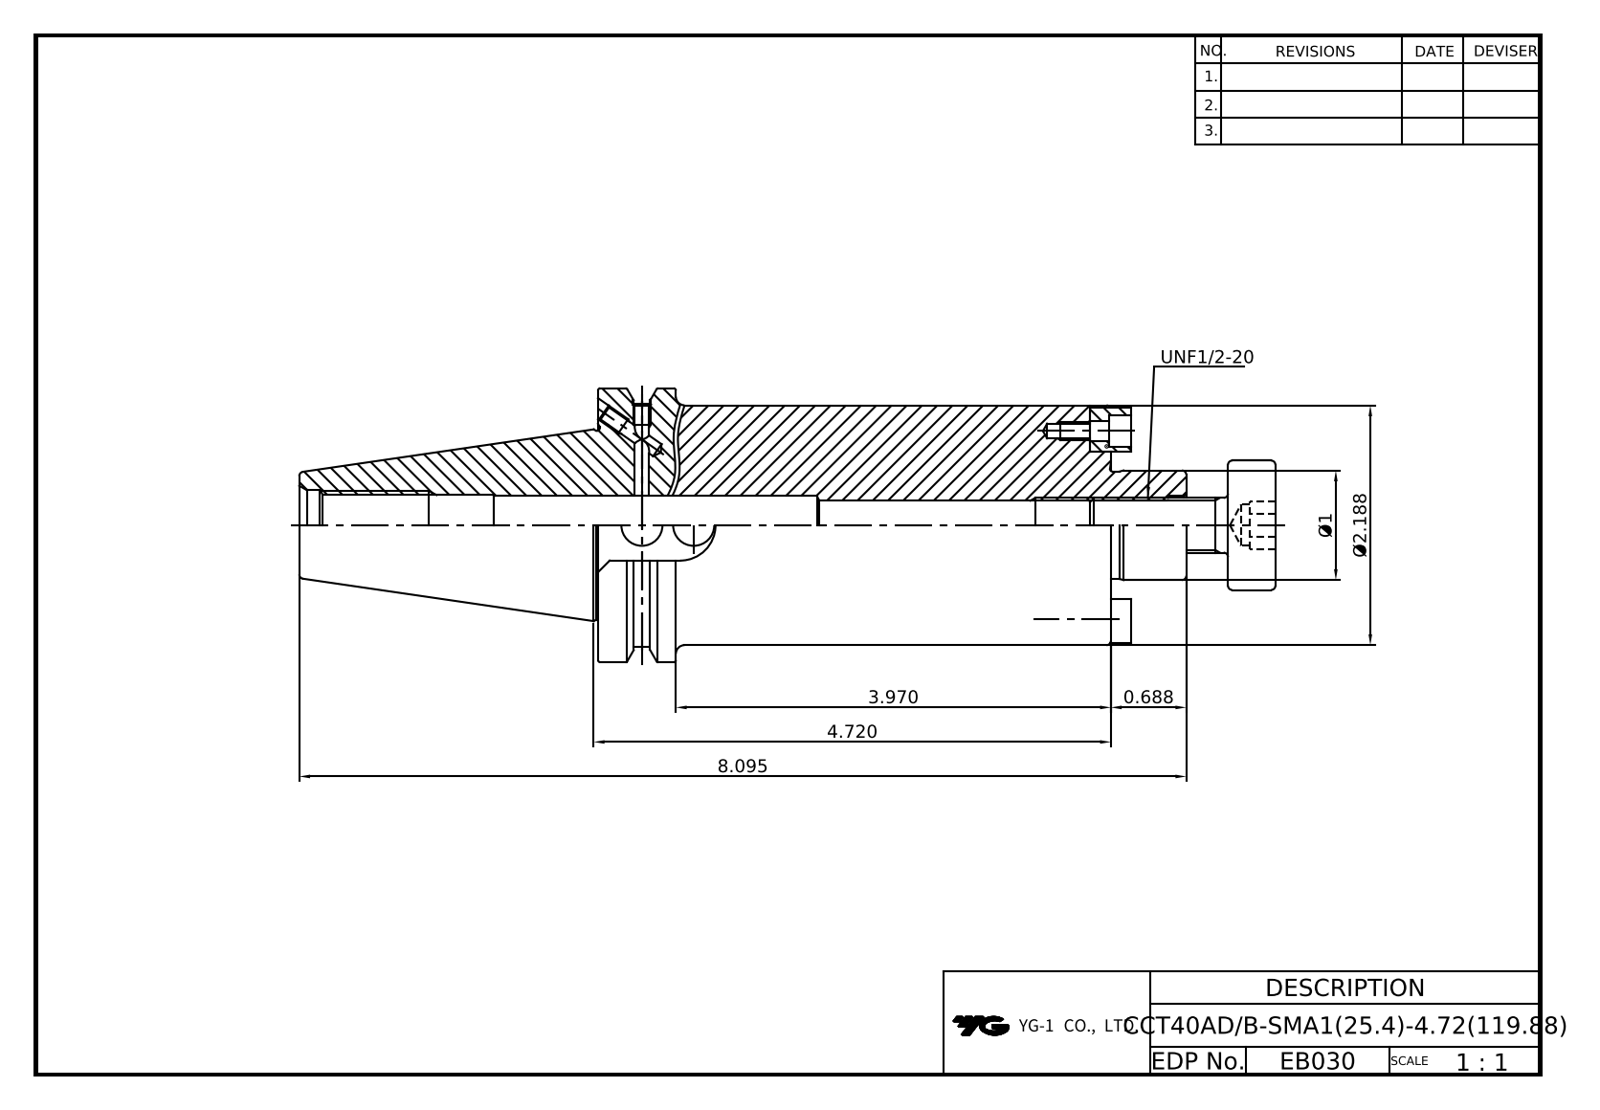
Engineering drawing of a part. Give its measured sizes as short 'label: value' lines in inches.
name: LO-CCT40ADB-SMA25.4-119.888; DRIVE KEY-9.52x9.52x10.2; HEX'' WRENCH BOLT-UNC#8-32x3_8L; COLLAR BOLT-UNF1_2-20x32L
written by: Autodesk Inventor 2022 (AUTOMOTIVE_DESIGN)
unit: in
bodies: 6 solids, 179 faces (87 planar, 49 cylindrical, 43 other)
size: 8.725 × 2.5 × 2.405
volume: 21.64 in³; area: 78.51 in²
holes: 4× ⌀0.128, 2× ⌀0.13, 2× ⌀0.157, 2× ⌀0.165, 2× ⌀0.177, 2× ⌀0.295, 2× ⌀0.375, 1× ⌀0.446, 1× ⌀0.512, 1× ⌀0.527, 1× ⌀0.531, 1× ⌀0.642
bosses: 2× ⌀0.27, 2× ⌀0.164, 1× ⌀2.5, 1× ⌀2.188, 1× ⌀1.724, 1× ⌀1.181, 1× ⌀1, 1× ⌀0.98
rounds: 2× R0.187, 1× R0.322, 1× R1.108
face distances: 4.681, 5.999, 1.318, 5.566, 0.885, 0.433, 0.375, 1.874, 4.493, 0.188
hole spacings: 0.86, 1.72
